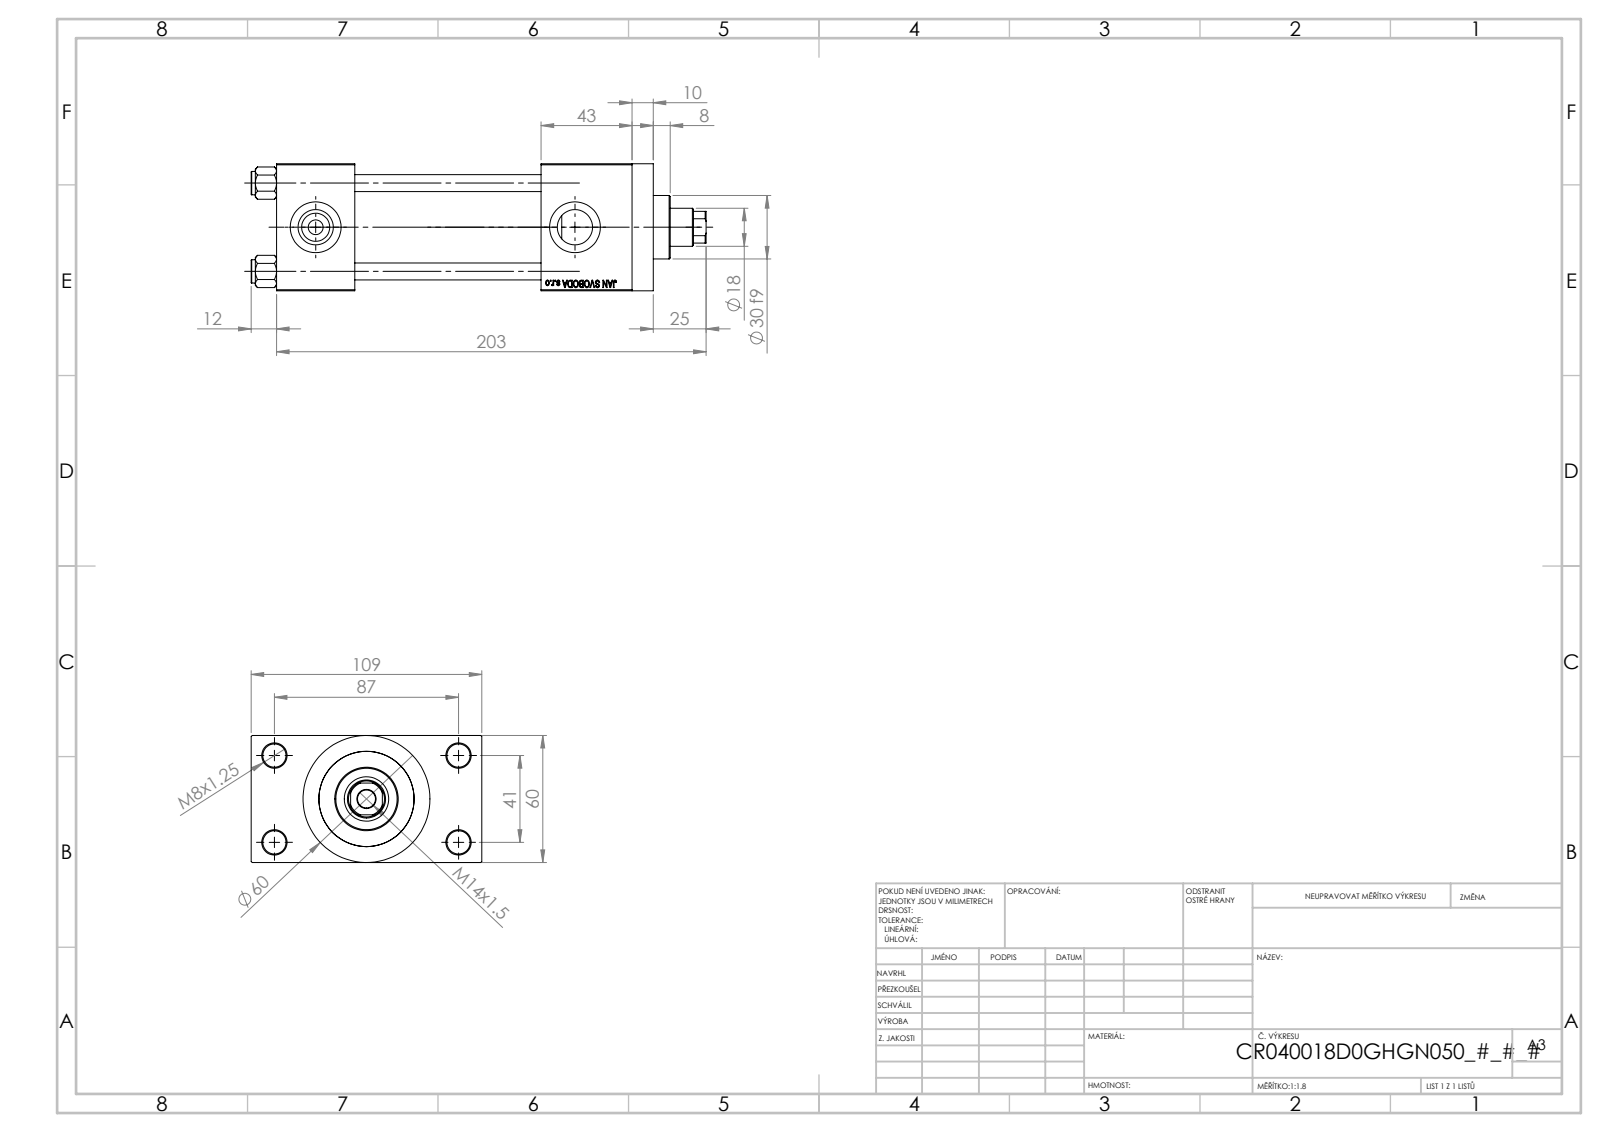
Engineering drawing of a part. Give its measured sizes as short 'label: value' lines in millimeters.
name: V215CR_D_Body; V215_VC_A; V215CR_VCP_D; NUT_M5_D (+1 more)
written by: SolidWorks 2019 (CONFIG_CONTROL_DESIGN)
unit: mm
bodies: 11 solids, 1104 faces (498 planar, 88 cylindrical, 518 other)
size: 215 × 109 × 60
volume: 538 346 mm³; area: 135 364 mm²
holes: 4× ⌀8, 4× ⌀11, 2× ⌀7, 2× ⌀16.66, 2× ⌀24, 1× ⌀8.5, 1× ⌀18, 1× ⌀21, 1× ⌀31, 1× ⌀40, 1× ⌀45
bosses: 4× ⌀11, 1× ⌀60, 1× ⌀46, 1× ⌀30
rounds: 1× R8.5
face distances: 60, 88, 24.5, 84.5, 37, 125, 168, 131, 43, 10
hole spacings: 22.65, 29.49, 41.7, 47.15, 48.09, 64.35, 76.49, 41
